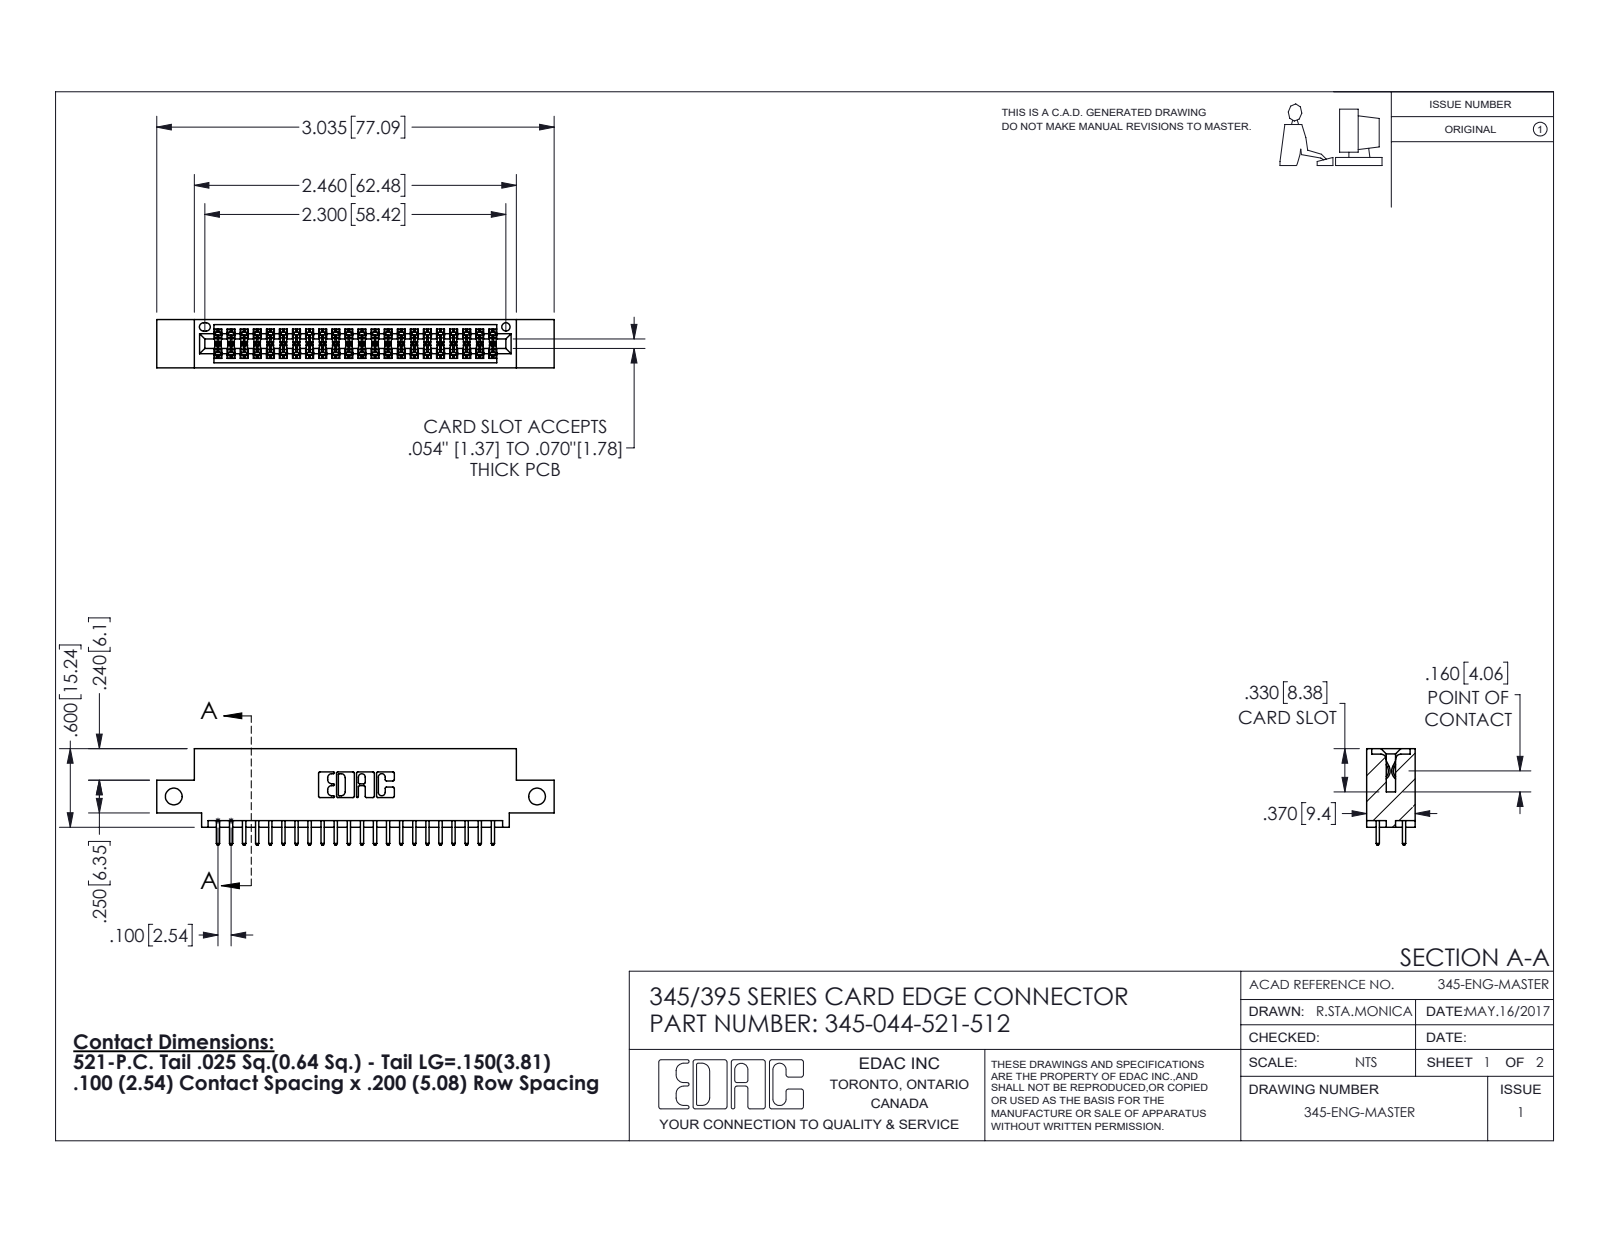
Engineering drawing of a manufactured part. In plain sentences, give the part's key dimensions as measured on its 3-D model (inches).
The part is named "345-044-521-512; 345-292-001_345-293-121; 345 Part_0.110 Offset - Side Mount". Its 3-D file was written by "SolidWorks 2016 (CONFIG_CONTROL_DESIGN)". It is 45 solids with 2330 faces: 1536 planar, 794 cylindrical and 0 other. Overall it measures 3.035 by 0.737 by 0.37 inches. Its volume is 0.435 cubic inches and its surface area 15.47 square inches. Round holes: 2 of diameter 0.128, 1 of diameter 0.064. Partial cylindrical surfaces (rounded edges, fillets, slot ends): 66 of radius 0.006, 44 of radius 0.01, 22 of radius 0.01, 6 of radius 0.007, 6 of radius 0.031, 3 of radius 0.026, 2 of radius 0.014, 2 of radius 0.019. The main face-to-face distances are 0.298, 0.072, 0.2, 0.37, 0.098, 0.272, 0.025, 0.225, 0.175, 0.149. The hole center spacings are 2.775.
